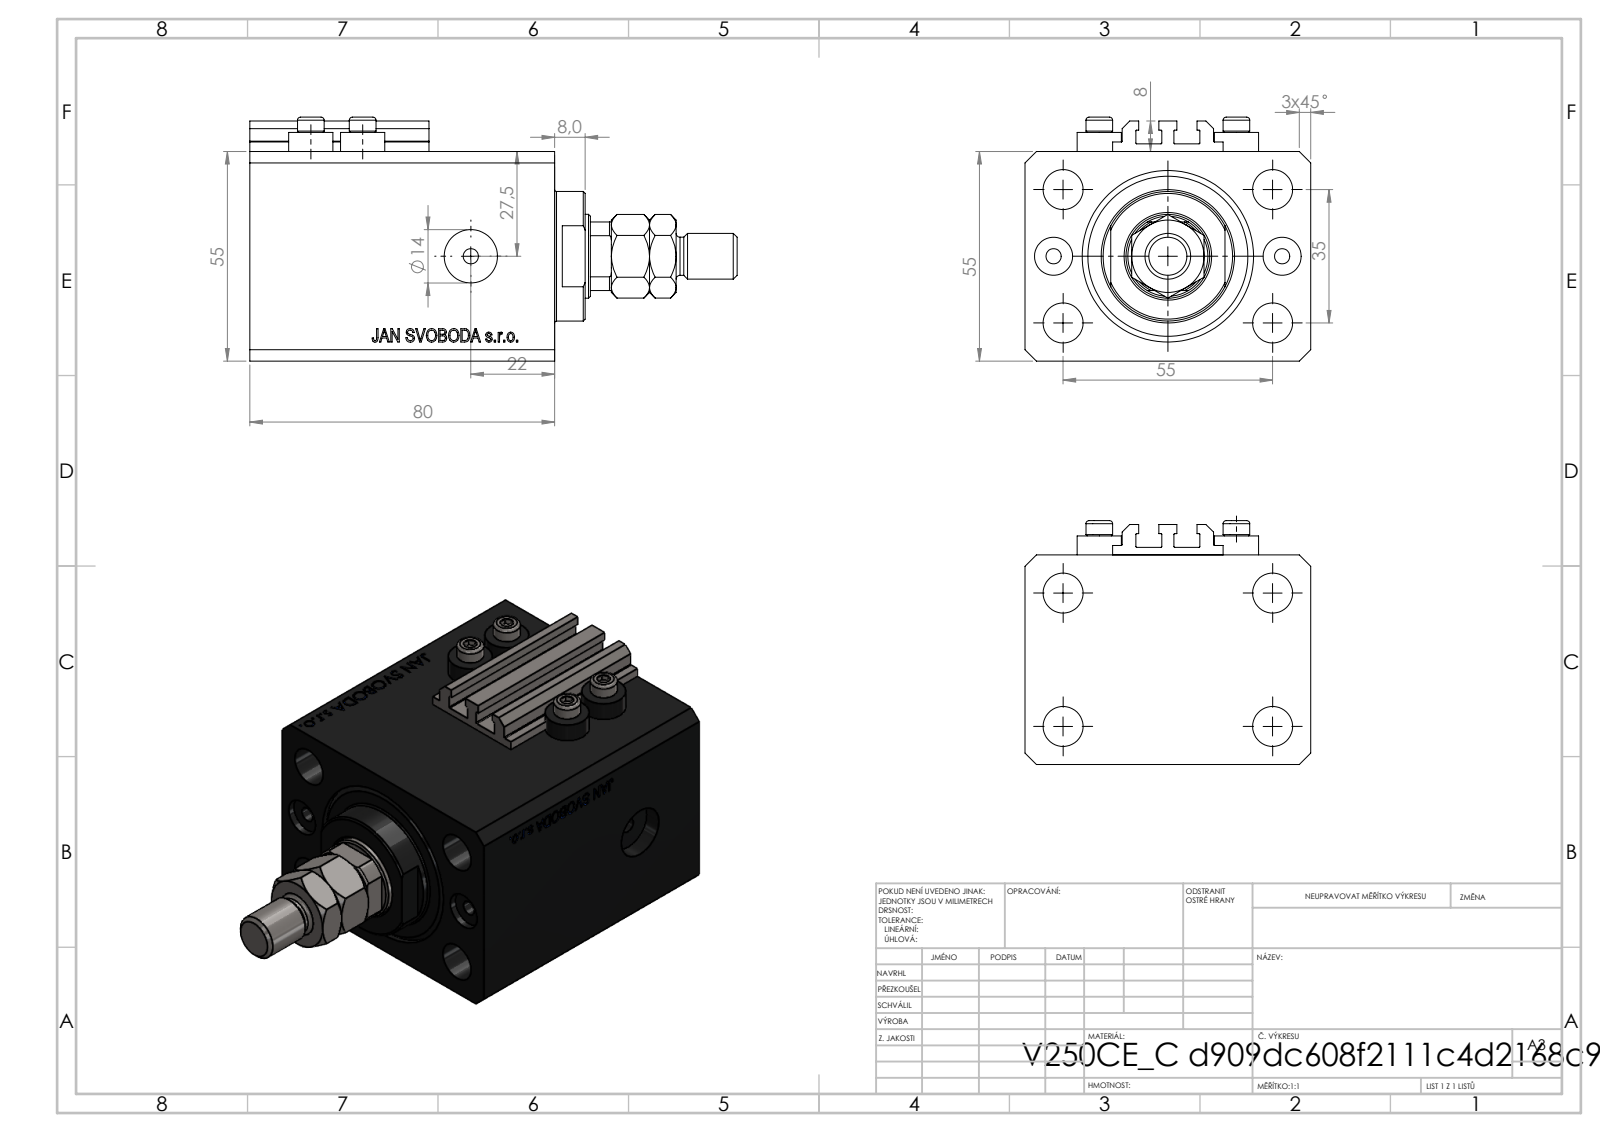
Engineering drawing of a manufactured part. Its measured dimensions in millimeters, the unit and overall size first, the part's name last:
Units: millimetres
Overall size (bounding box): 127.9 × 75 × 64
Round holes (diameter × count): ⌀4 ×8, ⌀10.5 ×5, ⌀10 ×2, ⌀14 ×2, ⌀22 ×1, ⌀32 ×1, ⌀45 ×1
Round bosses / shafts (diameter × count): ⌀11.6 ×4, ⌀7 ×4, ⌀34 ×1, ⌀12 ×1, ⌀10 ×1
Partial cylindrical surfaces — rounded edges, fillets, slot ends (radius × count): R0.2 ×10, R10.5 ×1
Main face-to-face distances: 55, 75, 80, 27.1, 52.9, 43, 9.9, 70.1, 3, 2.5
Hole centre spacings: 17.68, 32.6, 60.1, 36, 13.6, 30, 35, 38.48
Volume: 311 962 mm³ · Surface area: 76 430 mm²
Bodies: 9 solids, 1082 faces (518 planar, 90 cylindrical, 474 other)
Part name (STEP PRODUCT): MTA; V250CE_C; V250CE_VC_C; V250CE_C_VCP (+1 more)
STEP written by: SolidWorks 2019 (CONFIG_CONTROL_DESIGN)
